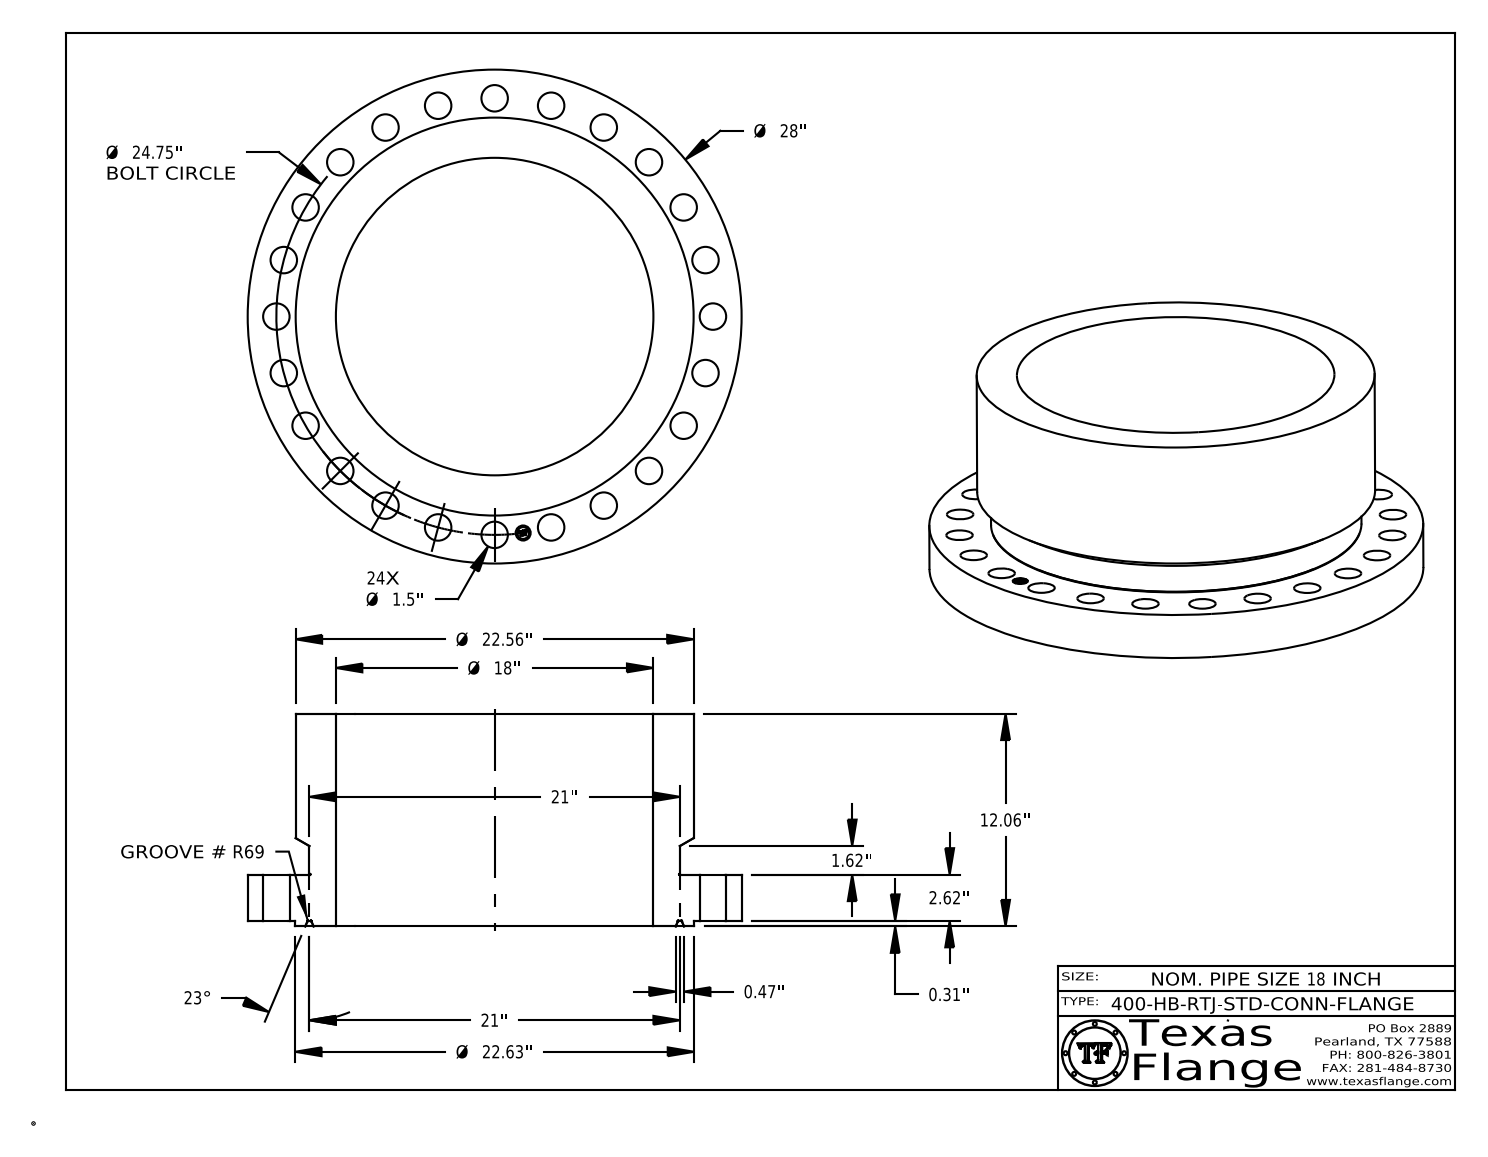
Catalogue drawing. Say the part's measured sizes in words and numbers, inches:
The part is named "18-400-HB-RTJ-STD-CONN-FLANGE". Its 3-D file was written by "CATIA V5 STEP AP214 (AUTOMOTIVE_DESIGN)". It is 1 solid with 463 faces: 371 planar, 78 cylindrical and 14 other. Overall it measures 28 by 28 by 12.063 inches. Its volume is 2 102 cubic inches and its surface area 2 620 square inches. Round holes: 24 of diameter 1.5, 1 of diameter 0.85, 1 of diameter 18. Round bosses or shafts: 8 of diameter 0.051, 1 of diameter 28, 1 of diameter 22.625, 1 of diameter 22.56, 1 of diameter 21, 1 of diameter 0.67. The main face-to-face distances are 2.62, 11.75, 9.13, 0.313, 2.933, 12.063, 2.928, 2.615, 9.135, 0.253. The hole center spacings are 12.375, 9.471, 15.067, 17.501, 21.434, 22.866, 23.906, 3.23.
